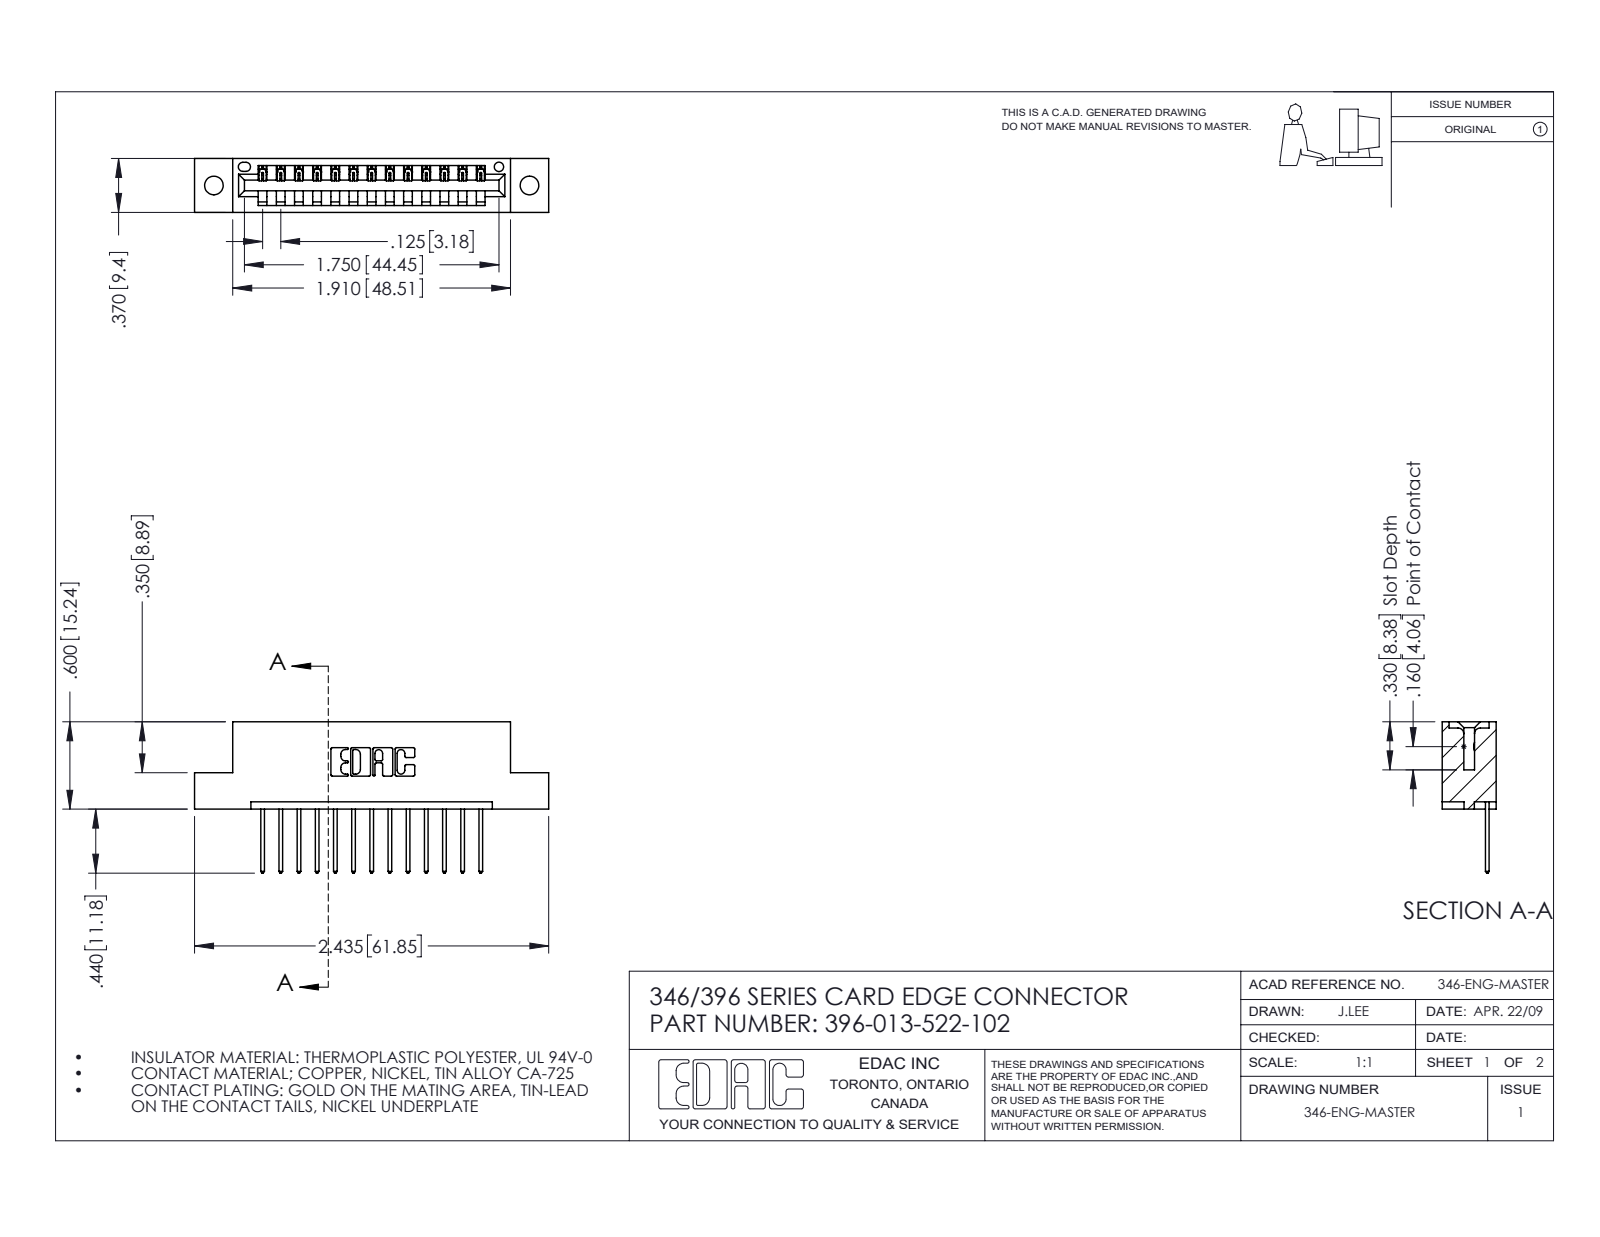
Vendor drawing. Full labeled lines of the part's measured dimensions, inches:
Part name (STEP PRODUCT): 345-292-001_345-293-122; 396-013-522-102; 346 Part_Flush Mounting Lugs - 0.128 Dia
STEP written by: SolidWorks 2016 (CONFIG_CONTROL_DESIGN)
Units: inches
Bodies: 14 solids, 876 faces (596 planar, 280 cylindrical, 0 other)
Overall size (bounding box): 2.435 × 1.04 × 0.37
Volume: 0.347 in³ · Surface area: 10.18 in²
Round holes (diameter × count): ⌀0.128 ×2, ⌀0.064 ×1
Partial cylindrical surfaces — rounded edges, fillets, slot ends (radius × count): R0.006 ×26, R0.01 ×26, R0.01 ×22, R0.007 ×6, R0.031 ×6, R0.026 ×3, R0.031 ×2, R0.04 ×2
Main face-to-face distances: 0.25, 0.048, 0.322, 0.37, 0.072, 0.298, 0.025, 0.148, 0.222, 0.1
Hole centre spacings: 0.246, 1.964, 2.17
